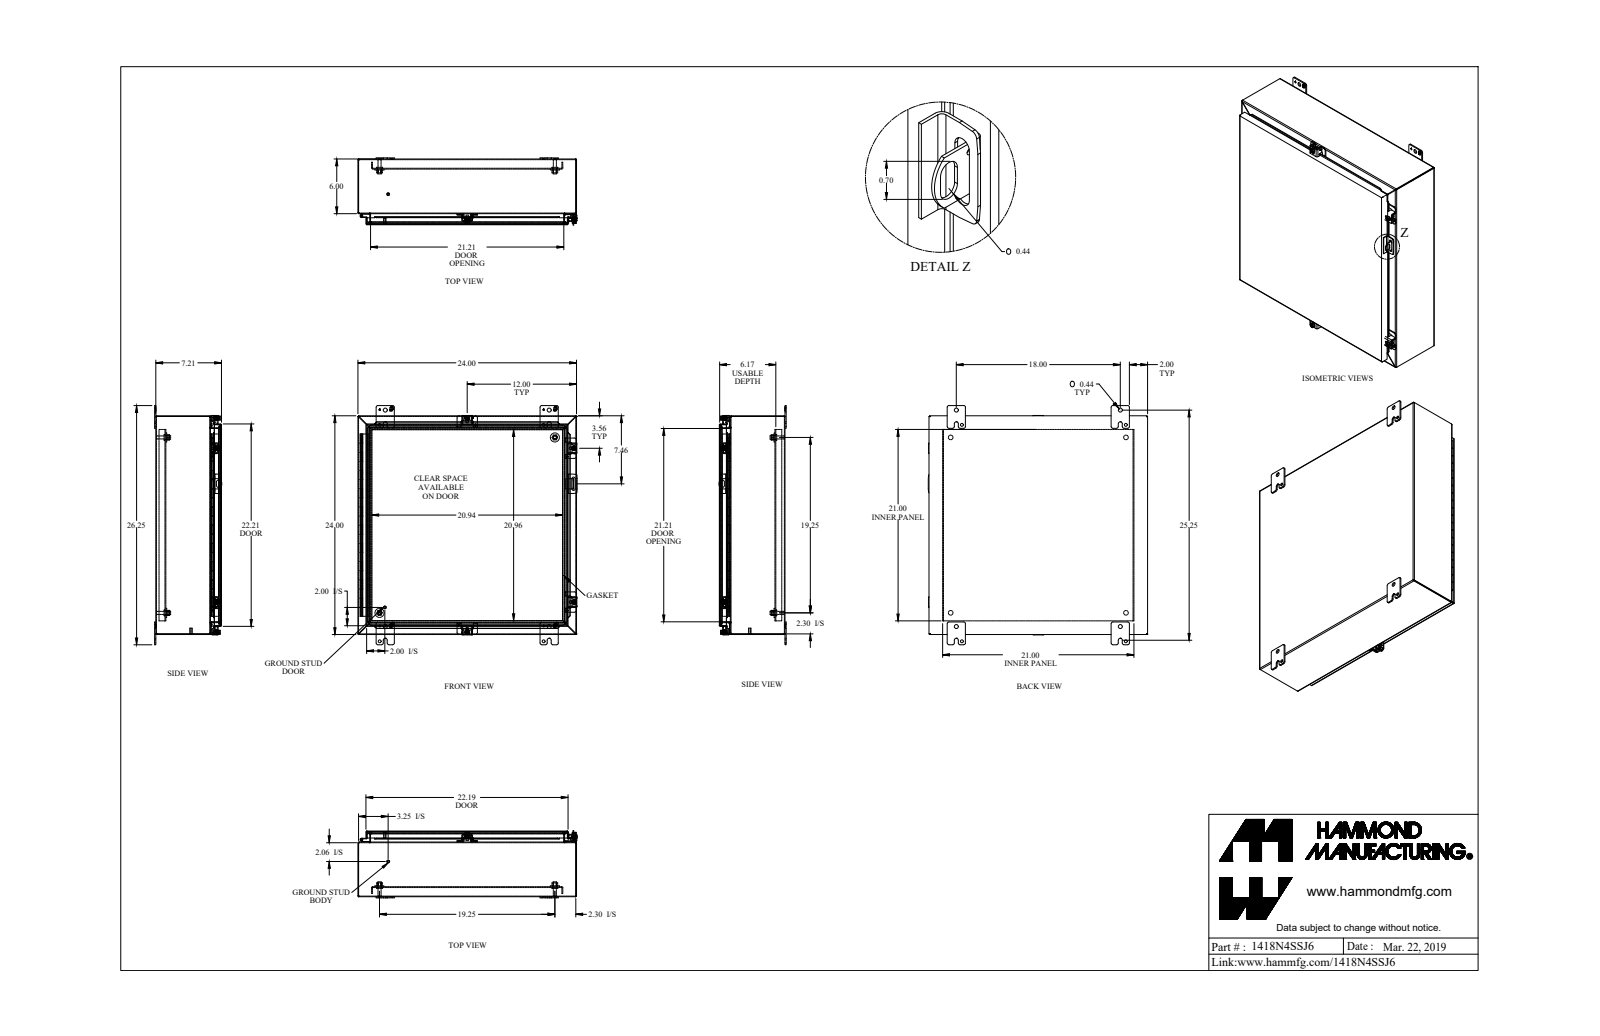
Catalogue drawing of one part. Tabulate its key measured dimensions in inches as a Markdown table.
| quantity | value |
| --- | --- |
| part name | 1418N4SSJ6_Default |
| STEP written by | SolidWorks 2019 (CONFIG_CONTROL_DESIGN) |
| units | inches |
| bodies | 39 solids, 1499 faces (925 planar, 481 cylindrical, 93 other) |
| overall size | 26.25 × 24.073 × 7.375 |
| volume | 199.6 in³ |
| surface area | 5 225 in² |
| round holes (diameter × count) | 0.213 × 4, 0.265 × 4, 0.313 × 4, 0.375 × 4, 0.437 × 4, 0.5 × 4, 0.307 × 2, 0.445 × 2, 0.125 × 1, 0.187 × 1 |
| round bosses / shafts (diameter × count) | 0.65 × 4, 0.5 × 4, 0.39 × 4, 0.375 × 4, 0.332 × 4, 0.244 × 4, 1 × 2, 0.313 × 2 |
| partial cylindrical surfaces (radius × count) | 0.188 × 26, 0.036 × 24, 0.108 × 24, 0.048 × 21, 0.143 × 21, 0.25 × 20, 0.125 × 10, 0.045 × 8 |
| main face-to-face distances | 0.072, 0.072, 23.928, 7.066, 7.138, 7.138, 7.21, 0.095, 6.106, 6.034 |
| hole center spacings | 19.25, 9.857, 18, 23.442, 1.735, 9.857, 18.685, 19.25 |
